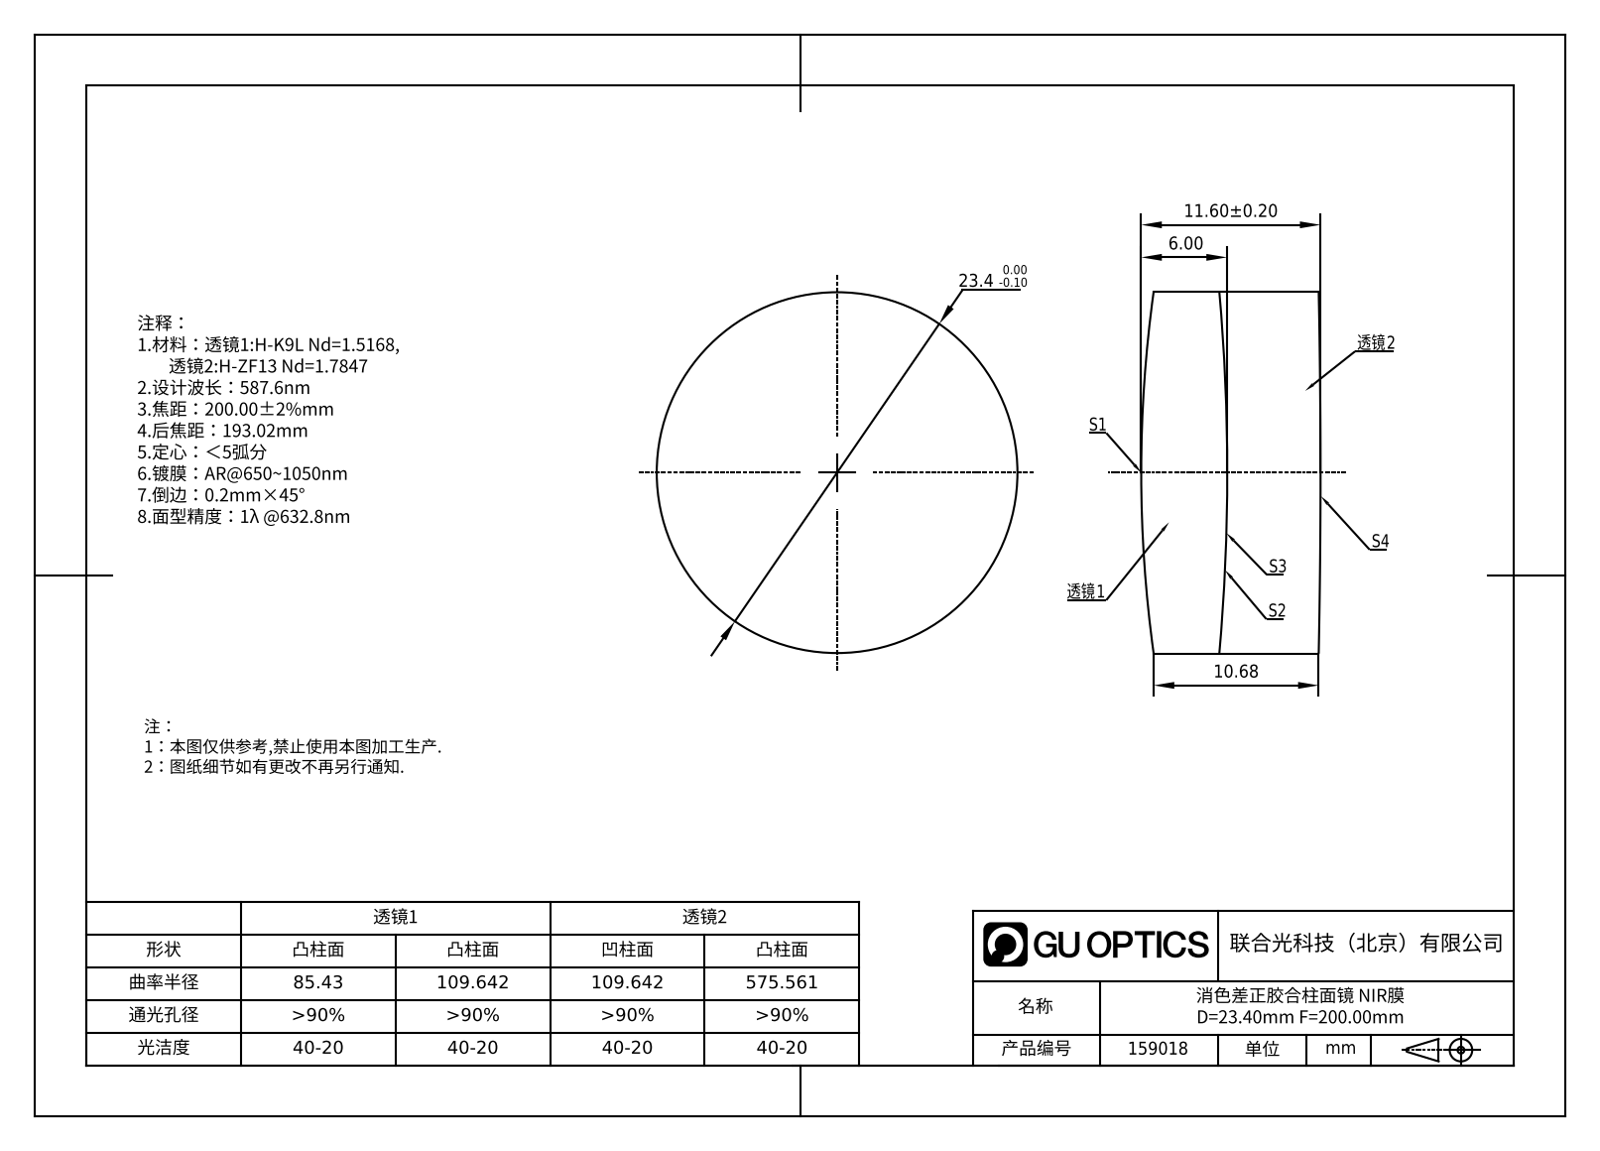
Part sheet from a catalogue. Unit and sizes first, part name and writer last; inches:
Units: inches
Overall size (bounding box): 0.921 × 0.921 × 0.457
Round bosses / shafts (diameter × count): ⌀0.921 ×1
Partial cylindrical surfaces — rounded edges, fillets, slot ends (radius × count): R3.363 ×1, R22.66 ×1
Volume: 0.298 in³ · Surface area: 2.604 in²
Bodies: 1 solid, 5 faces (0 planar, 5 cylindrical, 0 other)
Part name (STEP PRODUCT): 159018
STEP written by: SolidWorks 2020 (CONFIG_CONTROL_DESIGN)
